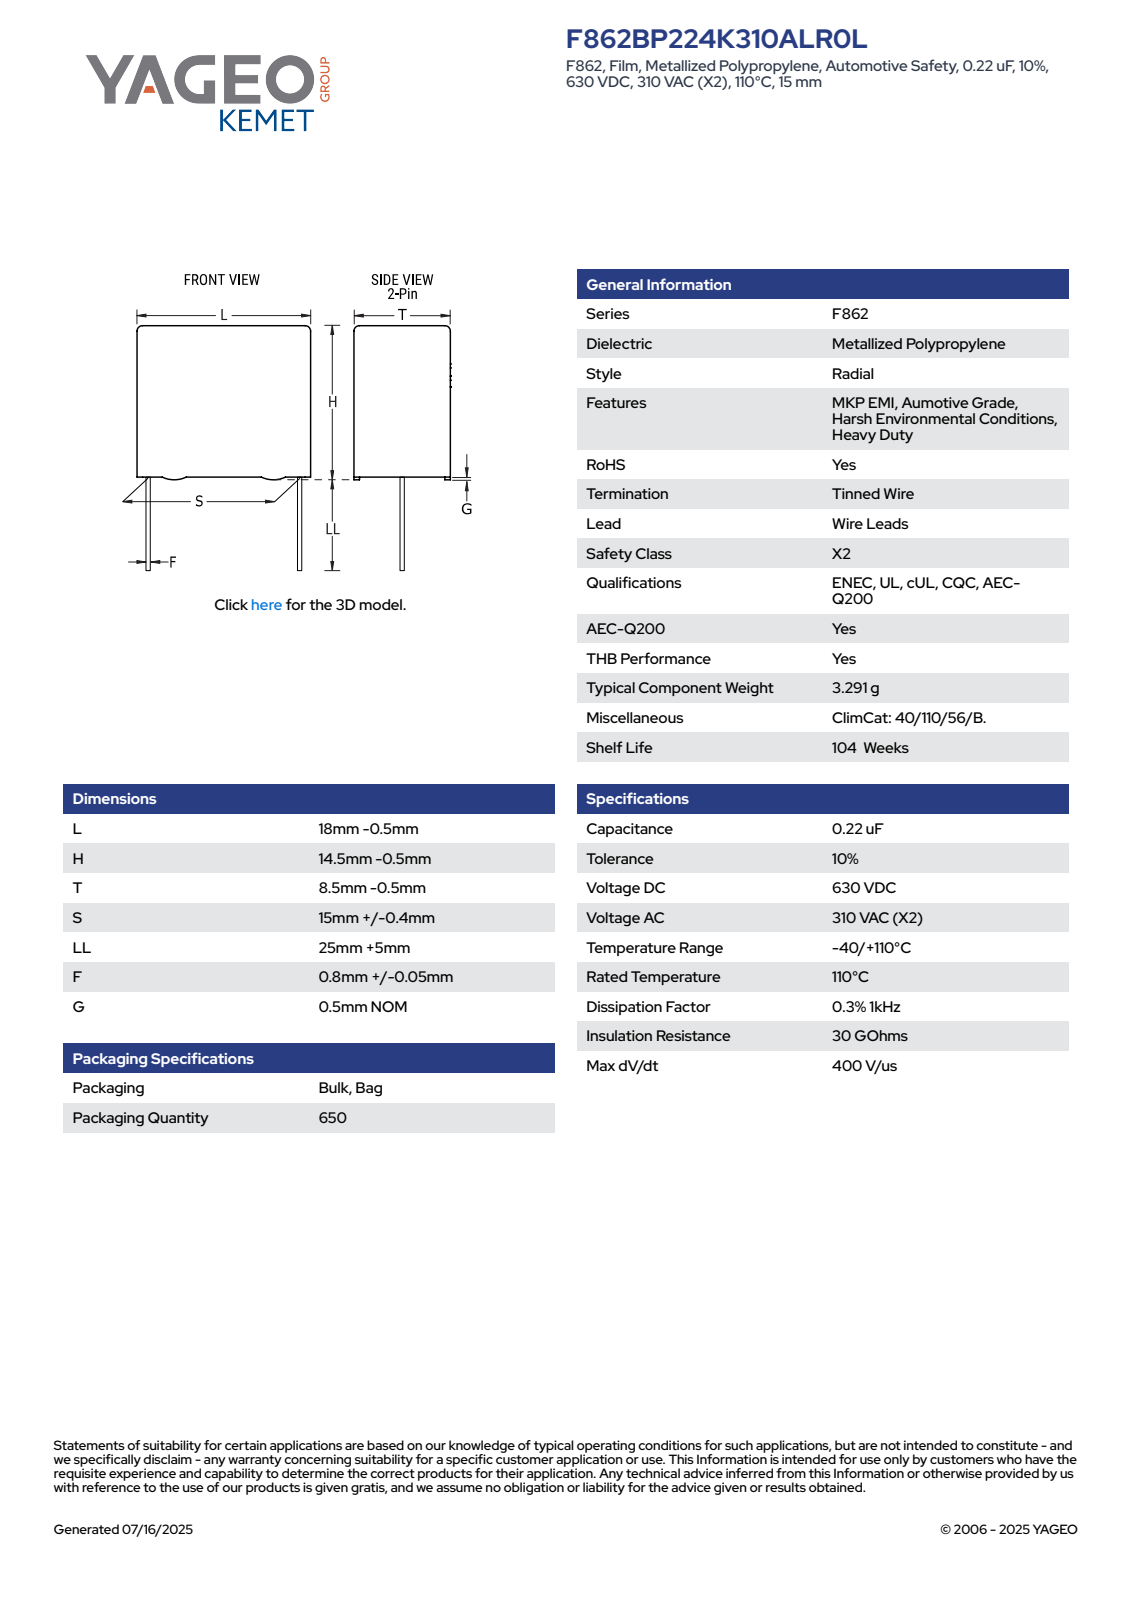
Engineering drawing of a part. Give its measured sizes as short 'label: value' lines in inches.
name: CFR_RBG_18X14.5X8.5_L17.5H14T8S15LL30F0.85G0.5
written by: SolidWorks 2014 (AUTOMOTIVE_DESIGN)
unit: in
bodies: 4 solids, 89 faces (81 planar, 8 cylindrical, 0 other)
size: 1.732 × 0.689 × 0.315
volume: 0.117 in³; area: 1.807 in²
bosses: 2× ⌀0.033
rounds: 4× R0.02
face distances: 0.315, 0.531, 0.689, 0.315, 0.018, 0.297, 0.02, 0.551, 0.019, 0.279
